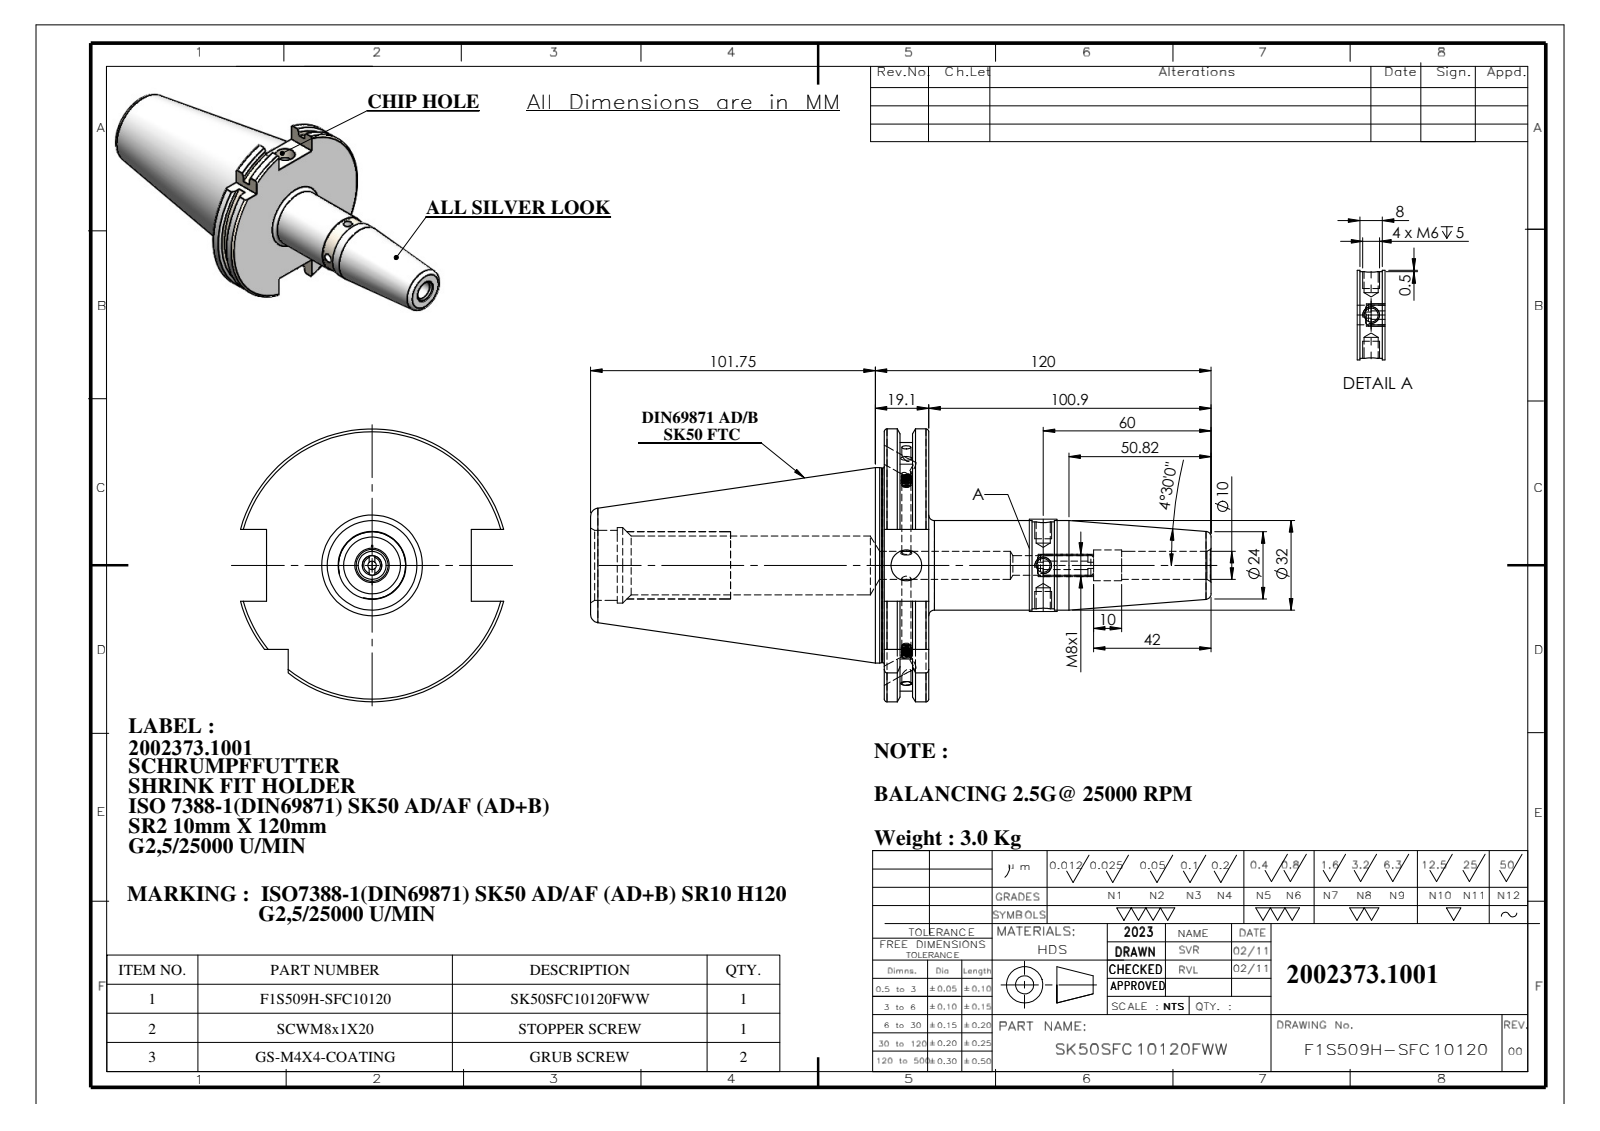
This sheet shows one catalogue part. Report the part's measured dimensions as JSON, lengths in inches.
{"part_name": "91506-SR210120", "step_written_by": "SolidWorks 2018 (AUTOMOTIVE_DESIGN)", "units": "inches", "bodies": {"solids": 1, "faces": 122, "planar": 29, "cylindrical": 53, "other": 40}, "overall_size": [8.73, 3.839, 3.703], "volume_in3": 24.49, "surface_area_in2": 85.28, "round_holes": [[0.197, 2], [0.236, 2], [0.433, 2], [0.13, 1], [0.276, 1], [0.393, 1], [0.827, 1], [0.984, 1], [1.063, 1]], "round_bosses_or_shafts": [[2.75, 1], [2.734, 1], [1.26, 1]], "partial_cylinders_radius": [[1.768, 1], [1.919, 1]], "face_to_face_distances": [0.626, 0.223, 0.403, 0.399, 0.176, 0.227, 4.132, 4.355, 4.531, 4.758], "hole_center_spacings": [1.925]}
